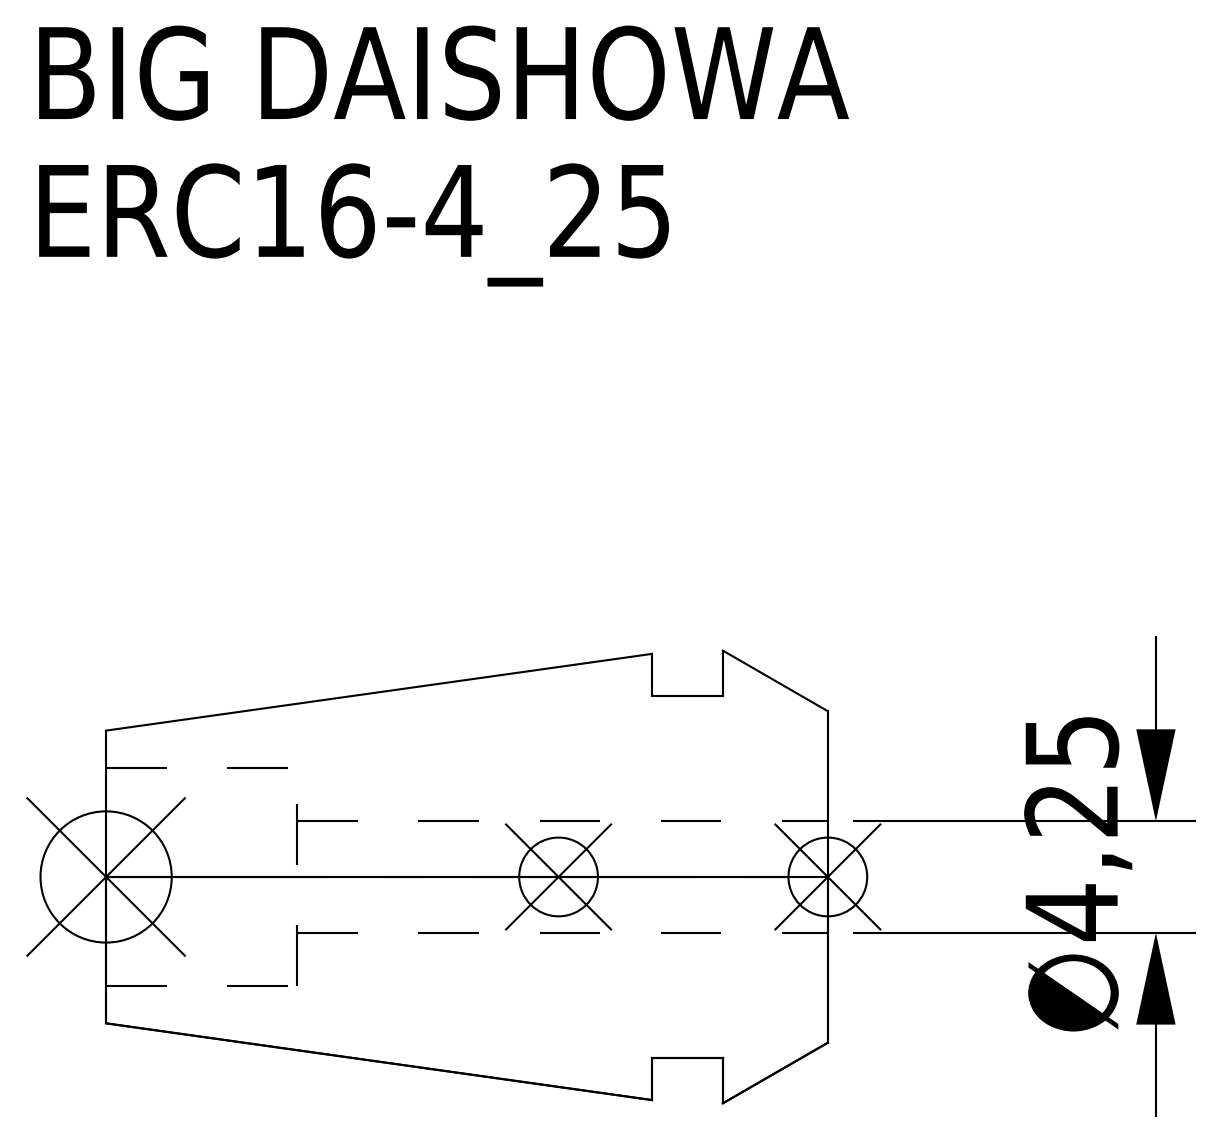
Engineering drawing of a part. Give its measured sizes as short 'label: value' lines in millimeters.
name: ERC16-4_25
written by: CREO PARAMETRIC BY PTC INC, 2016380 (AUTOMOTIVE_DESIGN)
unit: mm
bodies: 1 solid, 15 faces (5 planar, 6 cylindrical, 4 other)
size: 27.5 × 17.25 × 17.25
volume: 3 714 mm³; area: 2 079 mm²
holes: 1× ⌀4.25, 1× ⌀8.3
bosses: 1× ⌀13.8
face distances: 4, 6.7, 2.7, 27.5, 23.5, 20.8, 20.23, 16.23, 13.53, 7.27
